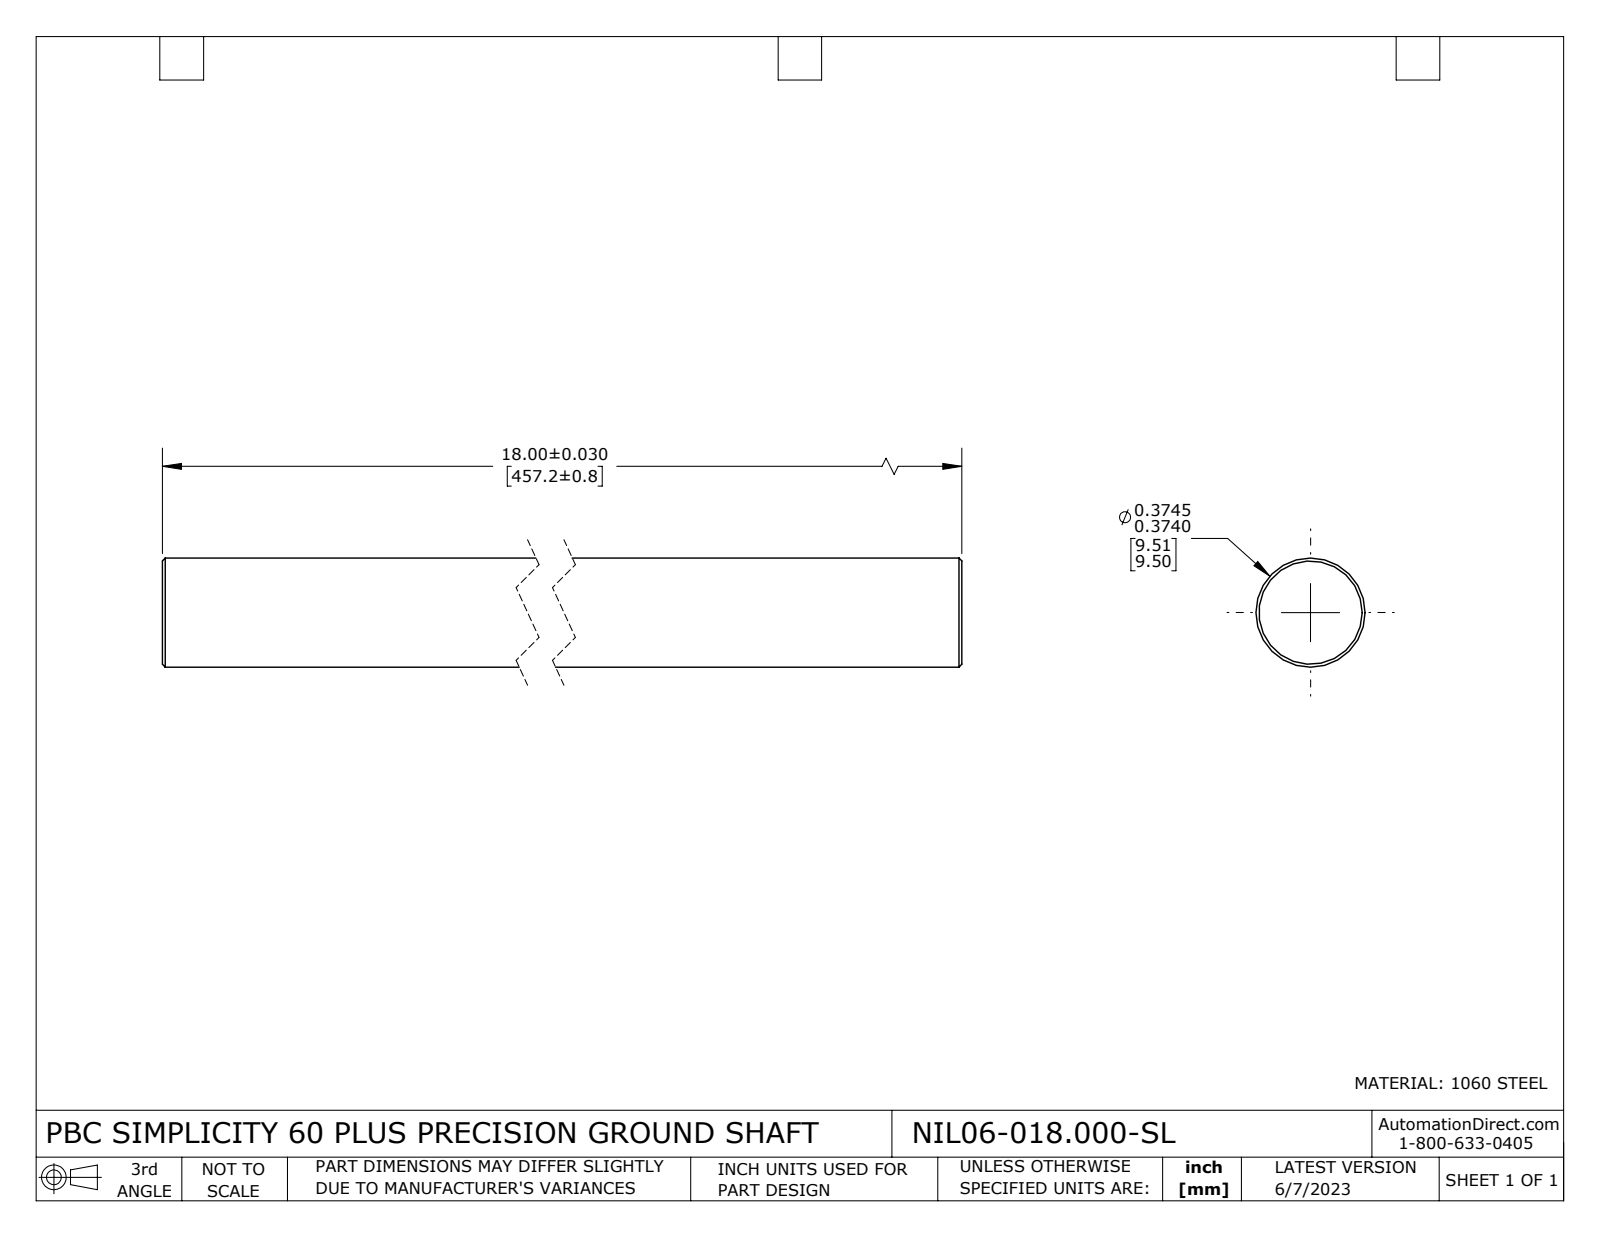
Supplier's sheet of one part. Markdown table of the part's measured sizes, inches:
| quantity | value |
| --- | --- |
| part name | NIL06-018.000-SL |
| STEP written by | SolidWorks 2021 (CONFIG_CONTROL_DESIGN) |
| units | inches |
| bodies | 1 solid, 8 faces (2 planar, 2 cylindrical, 4 other) |
| overall size | 18 × 0.375 × 0.375 |
| volume | 1.988 in³ |
| surface area | 21.41 in² |
| round bosses / shafts (diameter × count) | 0.375 × 1 |
| main face-to-face distances | 18 |
